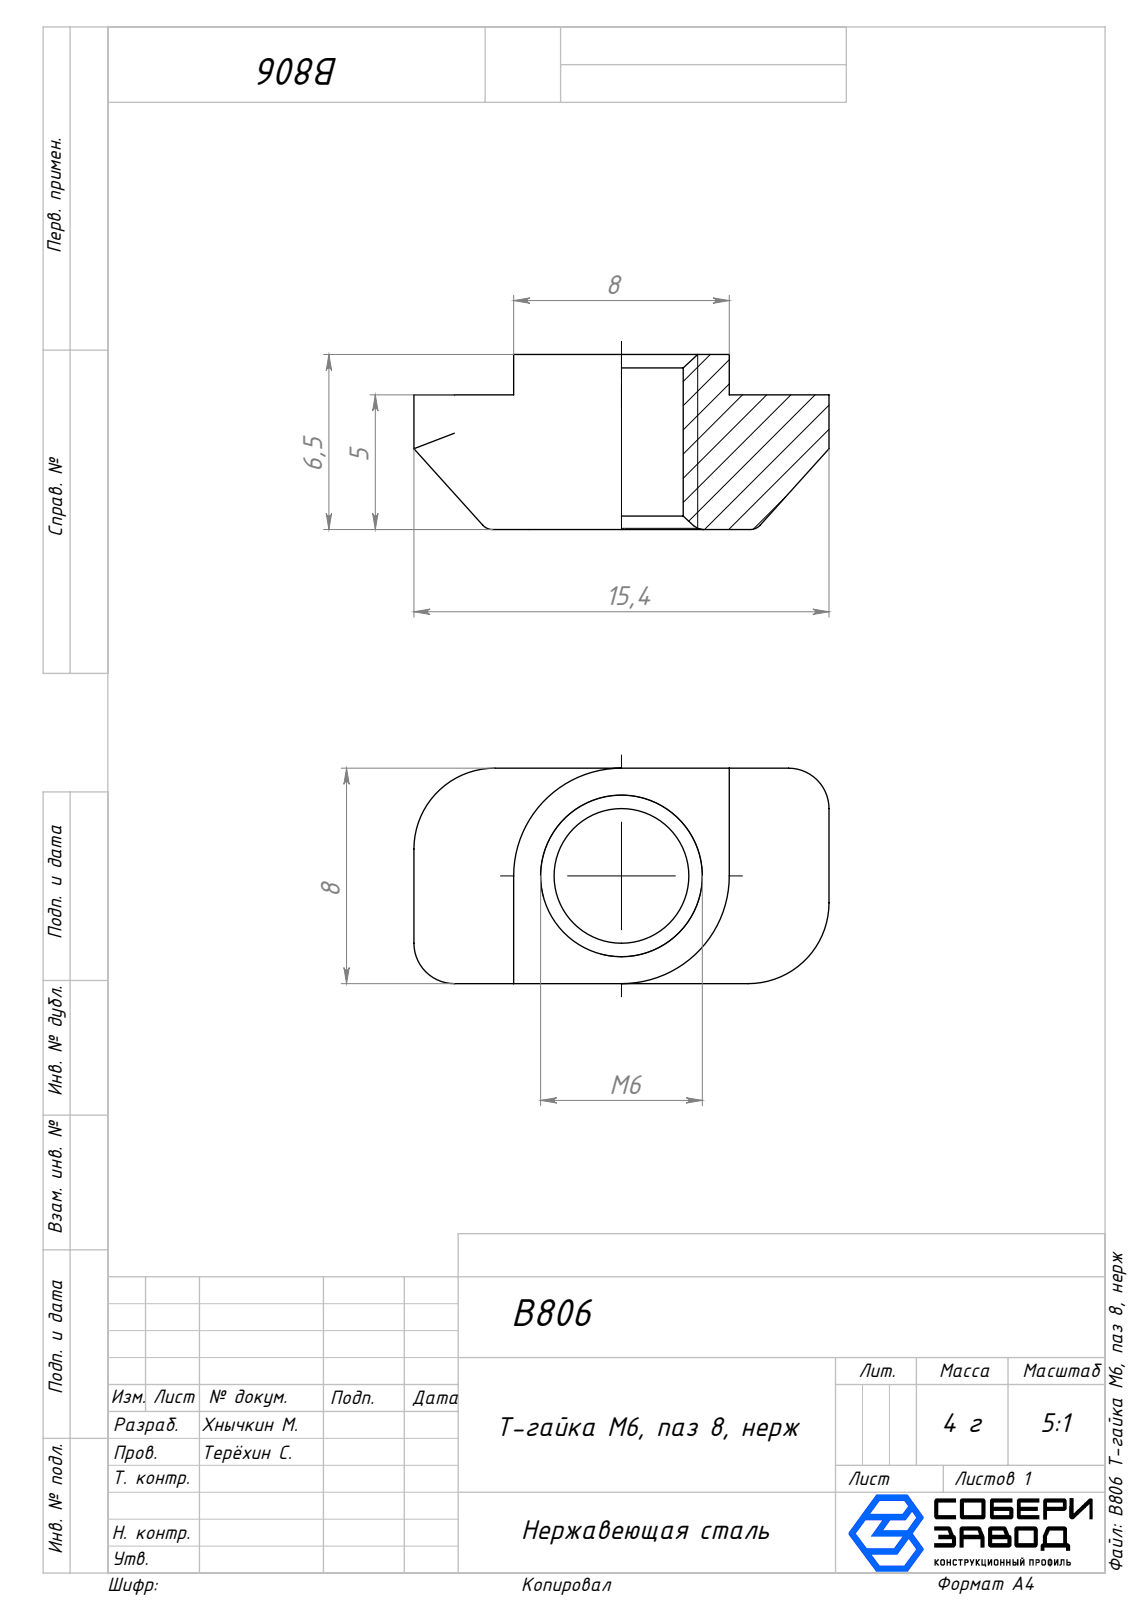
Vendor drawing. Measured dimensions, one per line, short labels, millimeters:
name: B806 Т-гайка М6, паз 8, нерж
written by: SolidWorks 2025 (AUTOMOTIVE_DESIGN)
unit: mm
bodies: 1 solid, 38 faces (12 planar, 16 cylindrical, 10 other)
size: 15.4 × 8 × 6.5
volume: 475 mm³; area: 496 mm²
holes: 1× ⌀5
rounds: 4× R0.5, 4× R1.5, 4× R3, 1× R4
face distances: 8, 5, 6.5, 1.5, 3.7, 11.7, 15.4
